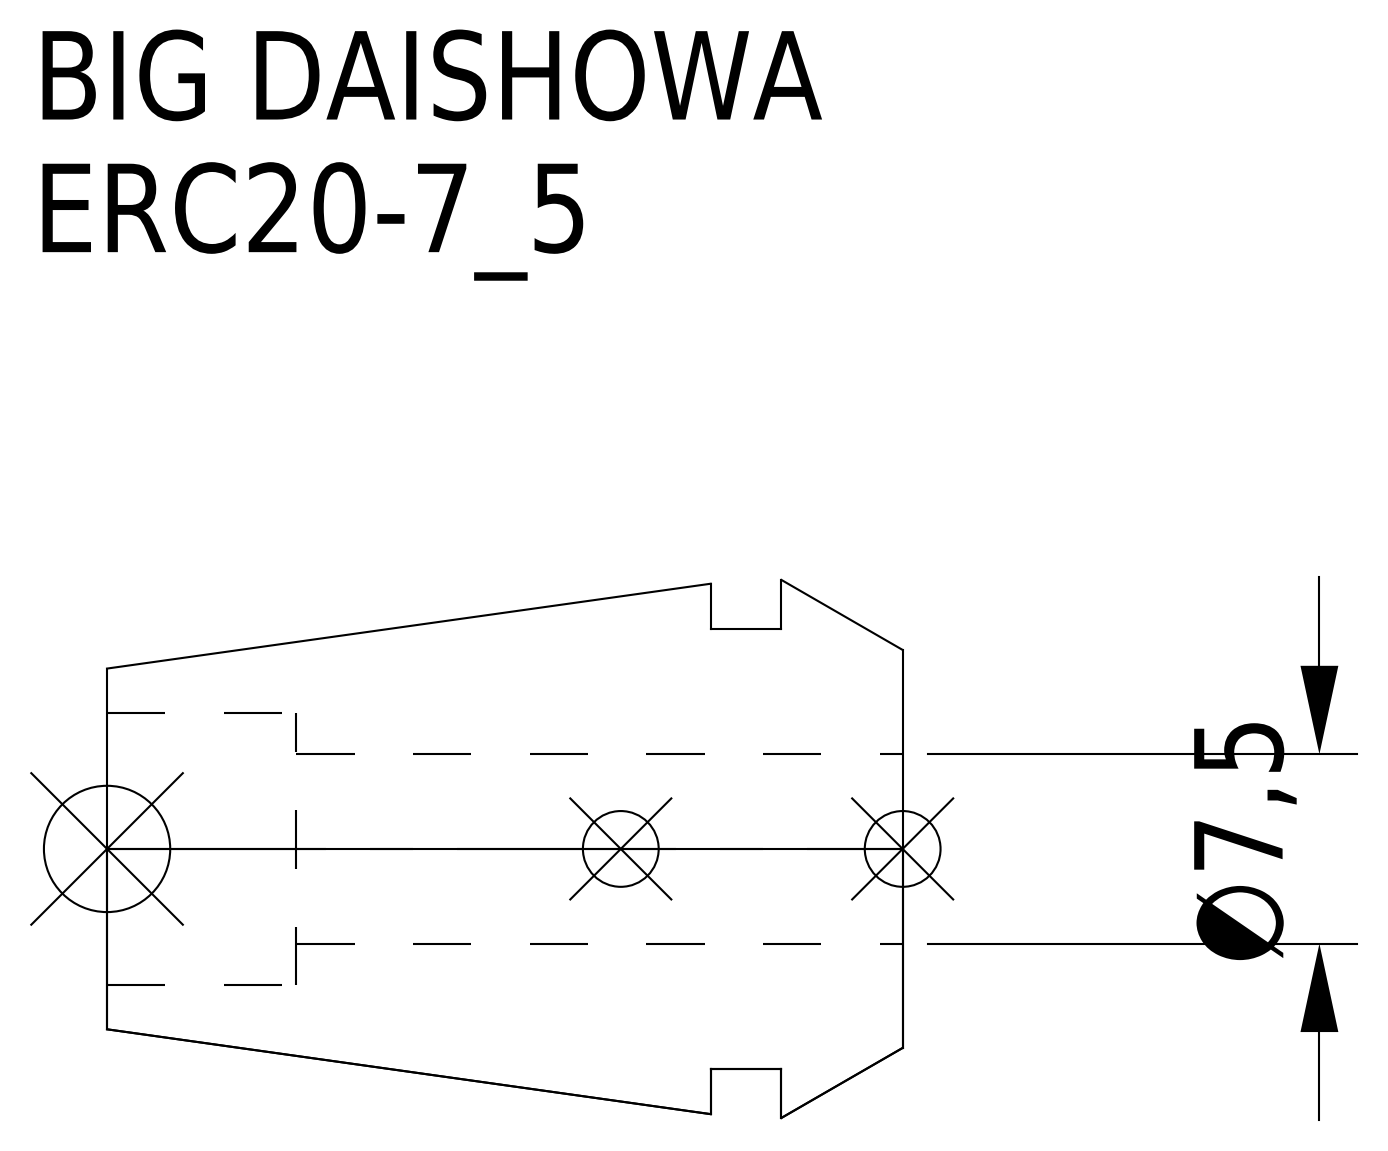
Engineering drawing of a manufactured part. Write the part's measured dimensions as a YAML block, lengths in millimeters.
part_name: "ERC20-7_5"
step_written_by: "CREO PARAMETRIC BY PTC INC, 2016380 (AUTOMOTIVE_DESIGN)"
units: millimeters
bodies: {solids: 1, faces: 15, planar: 5, cylindrical: 6, other: 4}
overall_size: [31.5, 21.3, 21.3]
volume: 6136
surface_area: 3127
round_holes:
  - {diameter: 7.5, count: 1}
  - {diameter: 10.8, count: 1}
round_bosses_or_shafts:
  - {diameter: 17.4, count: 1}
face_to_face_distances: [4.8, 7.6, 2.8, 31.5, 26.7, 23.9, 24.01, 19.21, 16.41, 7.49]
